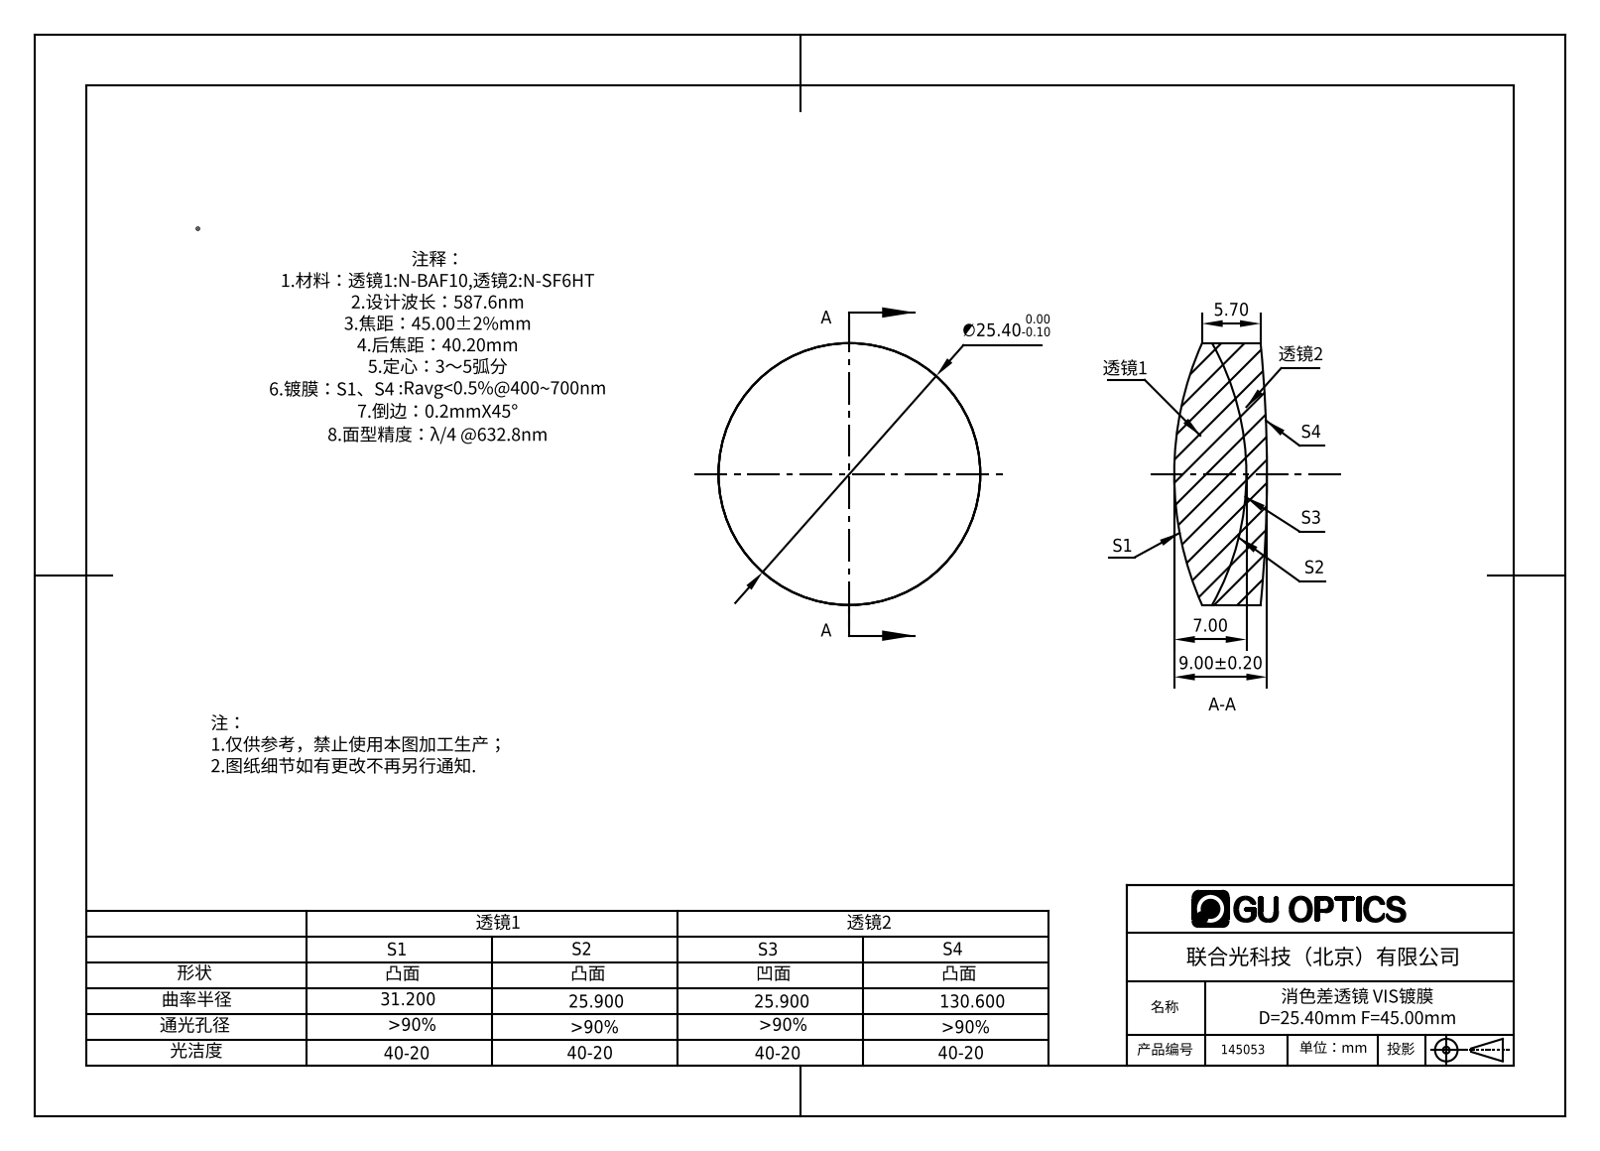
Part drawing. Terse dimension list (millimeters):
name: 145053
written by: SolidWorks 2016 (AUTOMOTIVE_DESIGN)
unit: mm
bodies: 2 solids, 12 faces (0 planar, 4 cylindrical, 8 other)
size: 25.4 × 25.4 × 9
volume: 3 729 mm³; area: 2 574 mm²
bosses: 1× ⌀25.4
